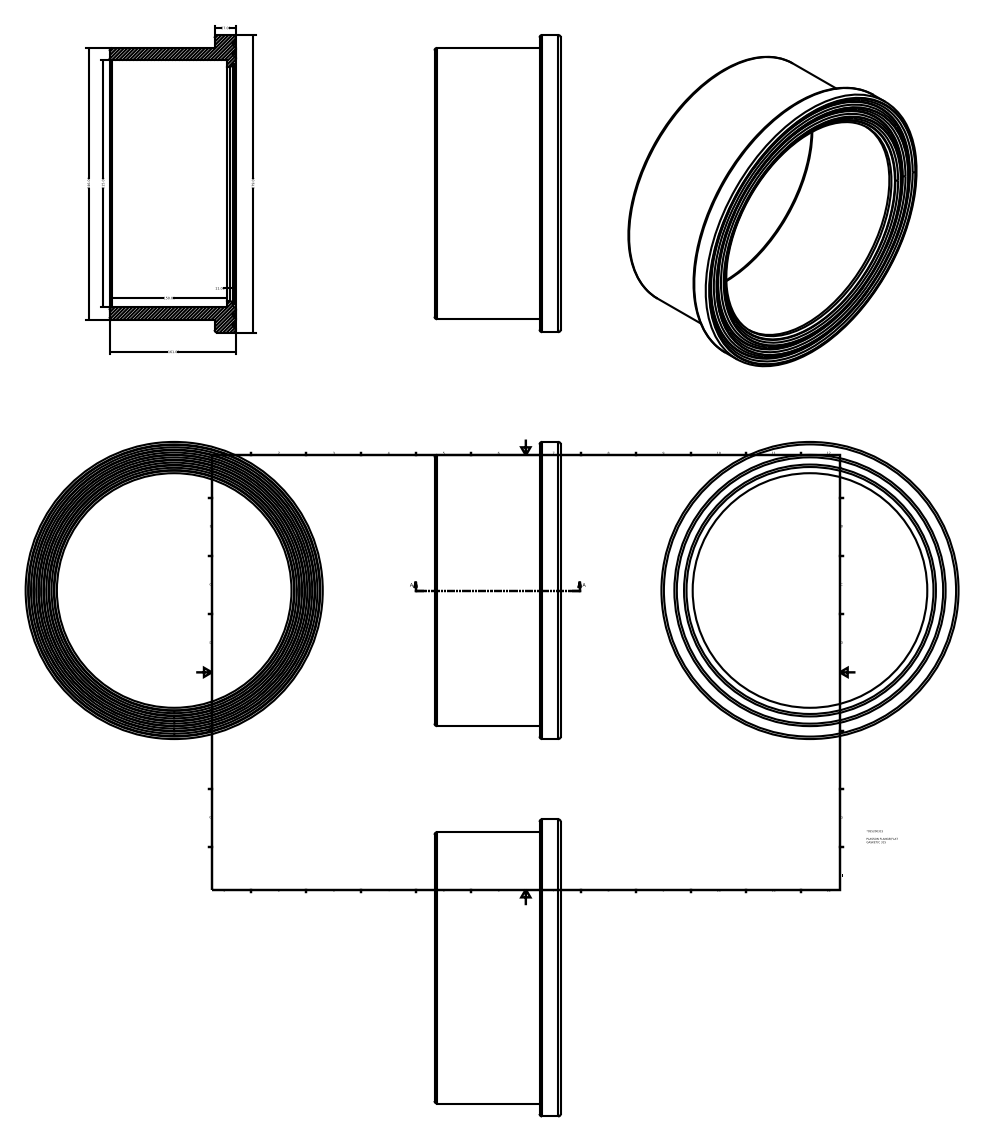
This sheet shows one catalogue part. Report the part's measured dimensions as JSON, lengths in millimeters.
{"part_name": "(_AS)055200315", "step_written_by": "Autodesk Inventor 2015 (AUTOMOTIVE_DESIGN)", "units": "millimeters", "bodies": {"solids": 1, "faces": 28, "planar": 9, "cylindrical": 4, "other": 15}, "overall_size": [379, 379, 161], "volume_mm3": 3085000, "surface_area_mm2": 419552, "round_holes": [[299.25, 1], [315, 1]], "round_bosses_or_shafts": [[379, 1], [346, 1]], "face_to_face_distances": [134, 150, 16, 156.95, 22.95, 6.95, 161, 27, 11, 4.05]}
